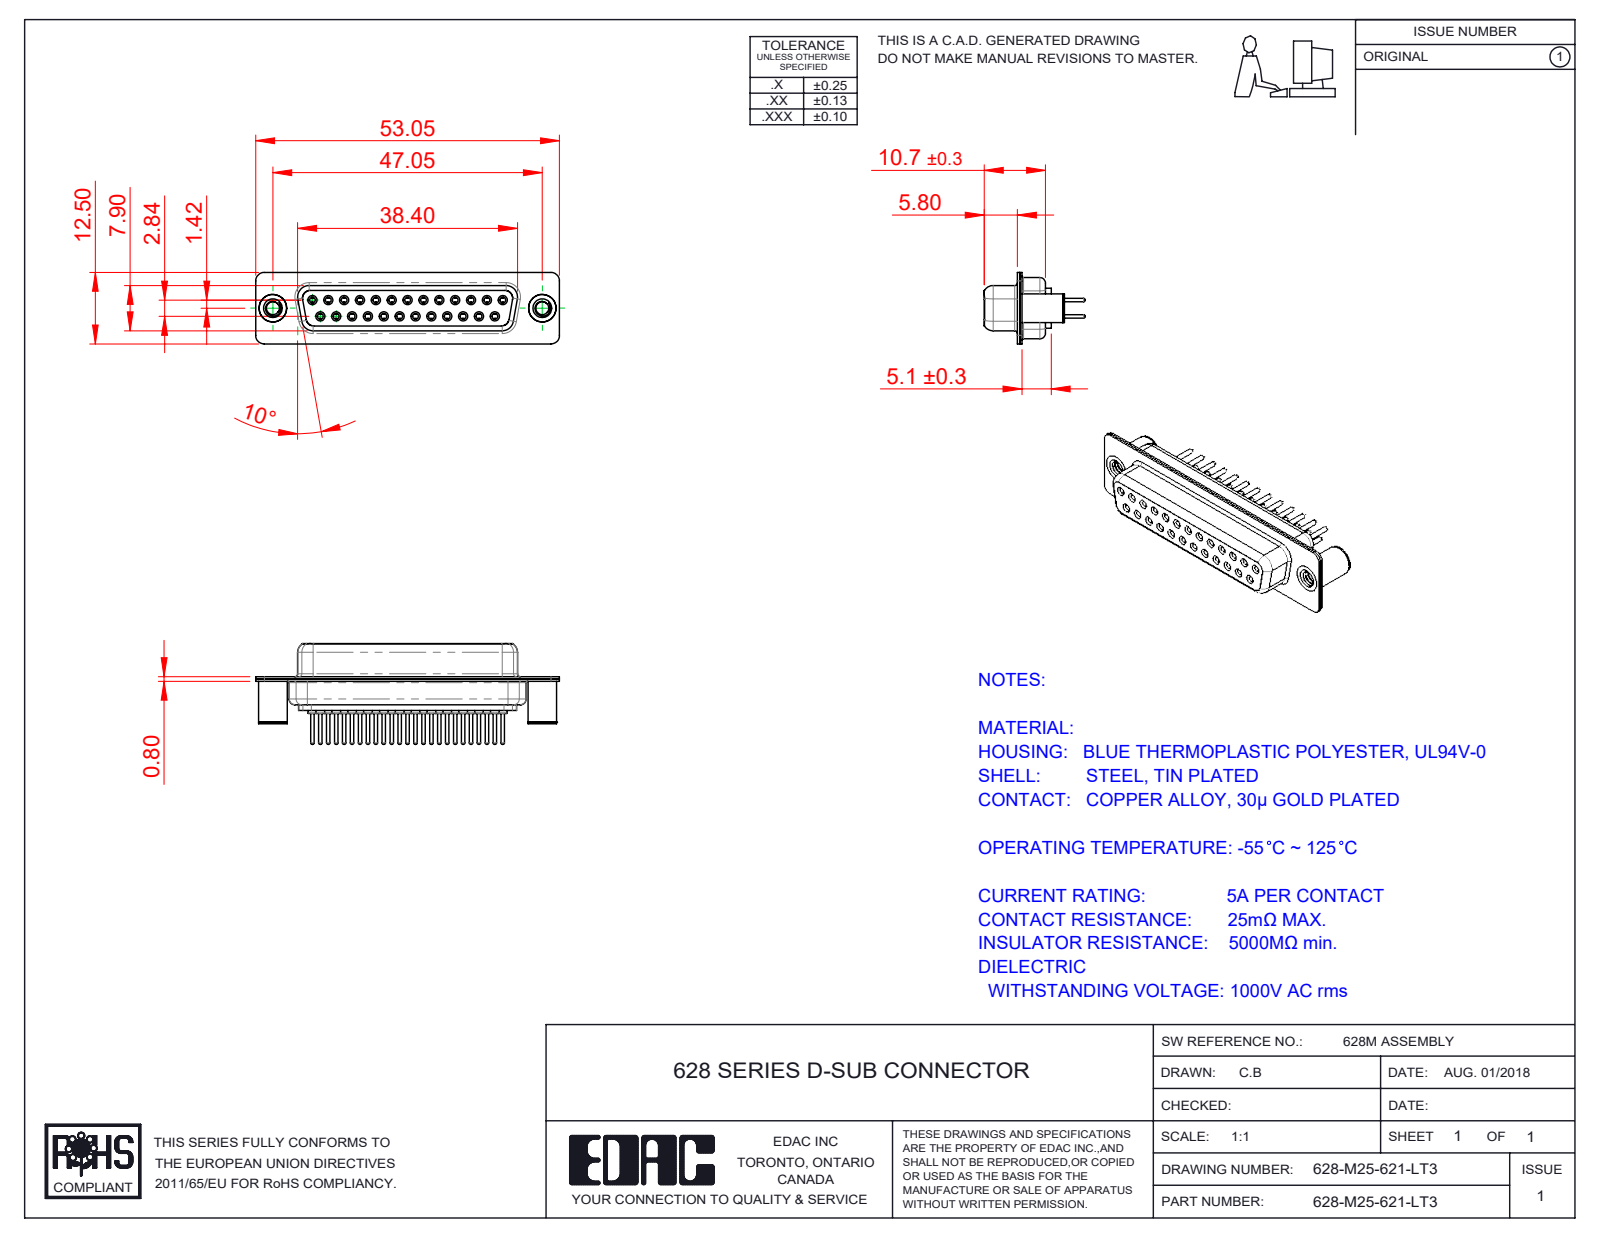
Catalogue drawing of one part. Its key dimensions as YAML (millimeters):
part_name: "628M Contact Row 2_21; 628M Shell Rear_25 Contacts; 628M Housing_25 Contacts; 628M Shell Front_25 Contacts (+3 more)"
step_written_by: "SolidWorks 2020 (CONFIG_CONTROL_DESIGN)"
units: millimeters
bodies: {solids: 30, faces: 1688, planar: 442, cylindrical: 636, other: 610}
overall_size: [53.05, 17.6, 12.5]
volume: 3863
surface_area: 9405
round_holes:
  - {diameter: 1, count: 25}
  - {diameter: 1.1, count: 25}
  - {diameter: 1.7, count: 25}
  - {diameter: 1.8, count: 25}
  - {diameter: 2, count: 25}
  - {diameter: 2.26, count: 2}
  - {diameter: 3.26, count: 2}
  - {diameter: 4, count: 2}
  - {diameter: 4.8, count: 2}
round_bosses_or_shafts:
  - {diameter: 2.2, count: 25}
  - {diameter: 1.6, count: 25}
  - {diameter: 1.5, count: 25}
  - {diameter: 0.6, count: 25}
  - {diameter: 5, count: 2}
  - {diameter: 4.9, count: 2}
partial_cylinders:
  - {radius: 1.5, count: 16}
  - {radius: 2, count: 12}
  - {radius: 1.35, count: 8}
  - {radius: 1.6, count: 8}
  - {radius: 0.25, count: 4}
  - {radius: 0.5, count: 4}
  - {radius: 0.6, count: 4}
  - {radius: 0.65, count: 4}
face_to_face_distances: [0.4, 1.4, 0.45, 8.45, 8.9, 1.8, 6.2, 7.05, 1, 1.85]
hole_center_spacings: [3.16, 2.77, 5.54, 8.31, 11.08, 13.85, 5.04, 7.49]
